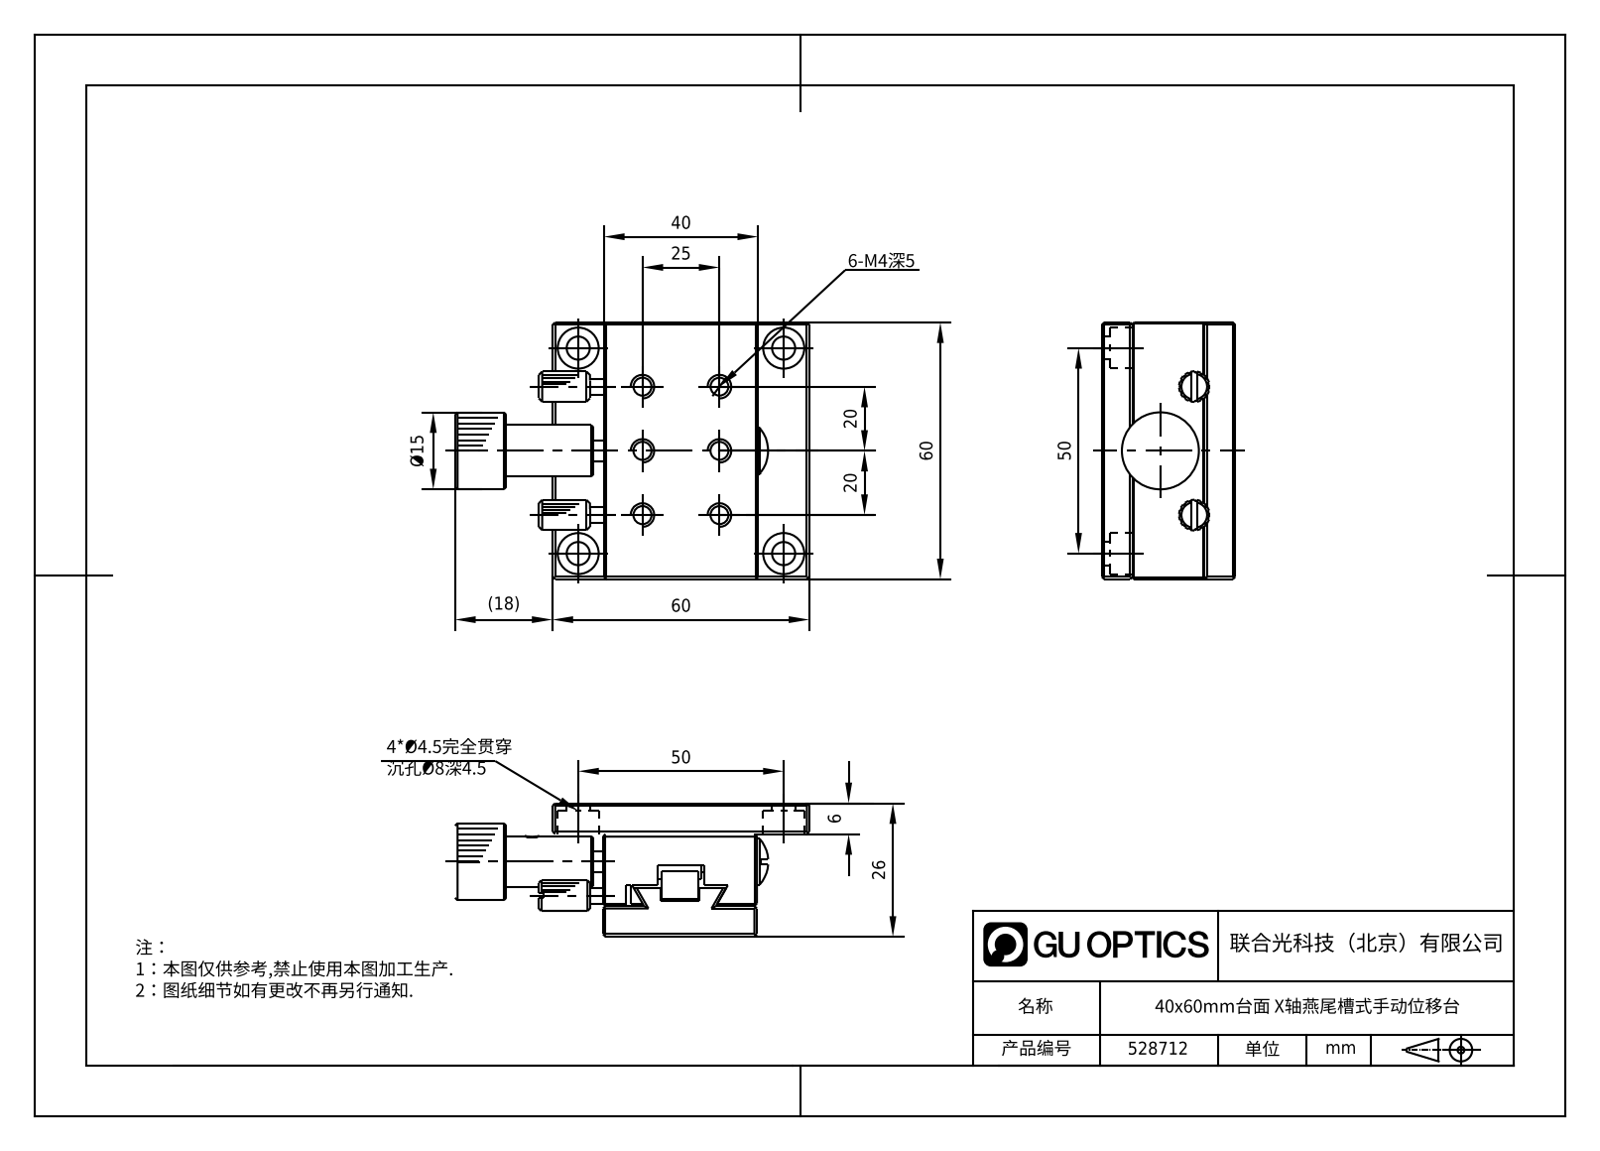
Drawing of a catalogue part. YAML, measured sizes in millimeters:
part_name: "528712"
step_written_by: "SolidWorks 2020 (CONFIG_CONTROL_DESIGN)"
units: millimeters
bodies: {solids: 12, faces: 670, planar: 368, cylindrical: 132, other: 170}
overall_size: [82.9, 60, 26]
volume: 68877
surface_area: 35064
round_holes:
  - {diameter: 4.5, count: 11}
  - {diameter: 8, count: 11}
  - {diameter: 2.5, count: 10}
  - {diameter: 3.3, count: 10}
  - {diameter: 2.05, count: 2}
  - {diameter: 2.8, count: 2}
  - {diameter: 4, count: 1}
  - {diameter: 4.1, count: 1}
round_bosses_or_shafts:
  - {diameter: 10, count: 2}
  - {diameter: 9, count: 2}
  - {diameter: 7, count: 2}
  - {diameter: 2.95, count: 2}
  - {diameter: 2.6, count: 2}
  - {diameter: 8, count: 1}
  - {diameter: 7.4, count: 1}
  - {diameter: 6.85, count: 1}
partial_cylinders:
  - {radius: 0.1, count: 2}
  - {radius: 10, count: 1}
face_to_face_distances: [6, 20, 10, 14, 5.5, 25.5, 19.5, 26, 60, 16]
hole_center_spacings: [27.95, 15.21, 31.32, 41.23, 45.07, 5.59, 13.46, 14.14]
